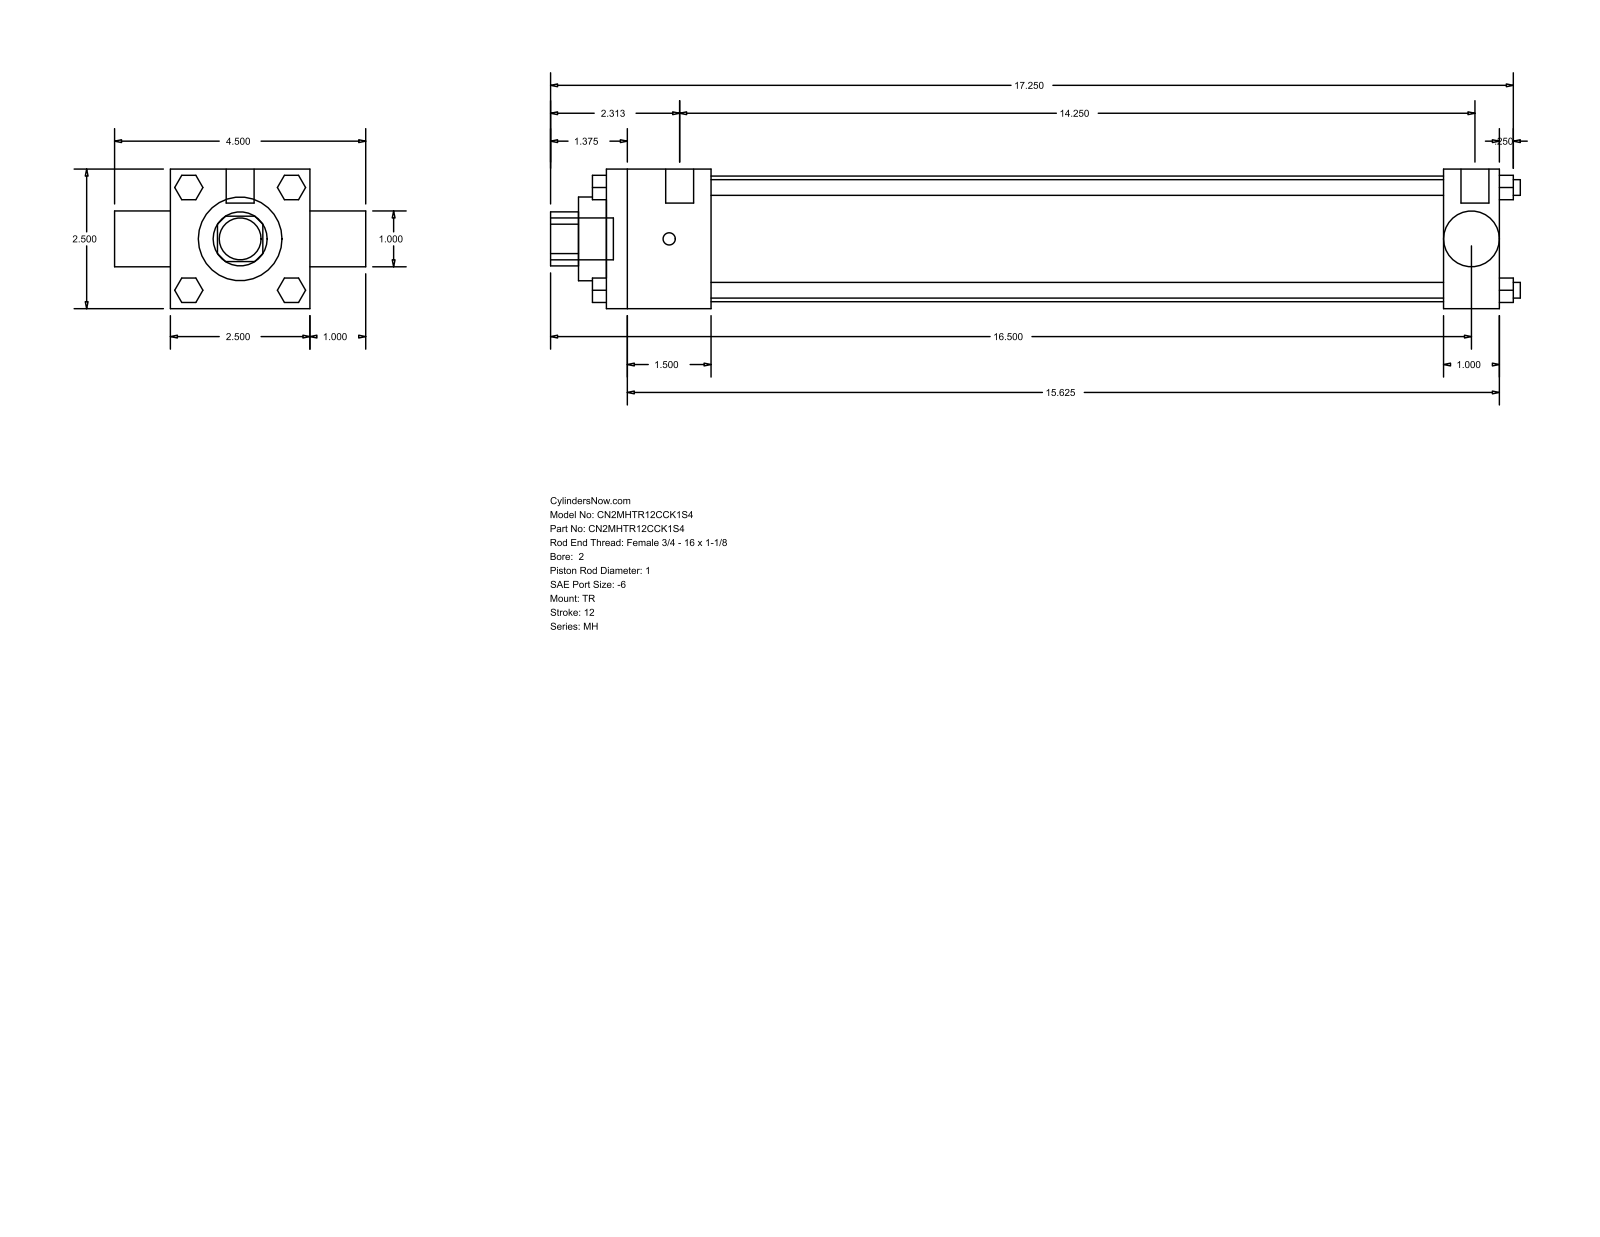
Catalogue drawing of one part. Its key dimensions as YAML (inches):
part_name: "MH_TR__0200_1"
step_written_by: "GSSL Pune (CONFIG_CONTROL_DESIGN)"
units: inches
bodies: {solids: 0, faces: 120, planar: 92, cylindrical: 28, other: 0}
overall_size: [17.375, 4.5, 2.5]
round_holes:
  - {diameter: 0.998, count: 1}
  - {diameter: 1, count: 1}
  - {diameter: 1.5, count: 1}
  - {diameter: 2.25, count: 1}
round_bosses_or_shafts:
  - {diameter: 0.281, count: 4}
  - {diameter: 0.219, count: 3}
  - {diameter: 0.5, count: 2}
  - {diameter: 0.75, count: 1}
partial_cylinders:
  - {radius: 0.484, count: 1}
face_to_face_distances: [2.5, 16, 1, 1.875, 15, 13.125, 14.125, 3.5, 16.5, 0.25]
